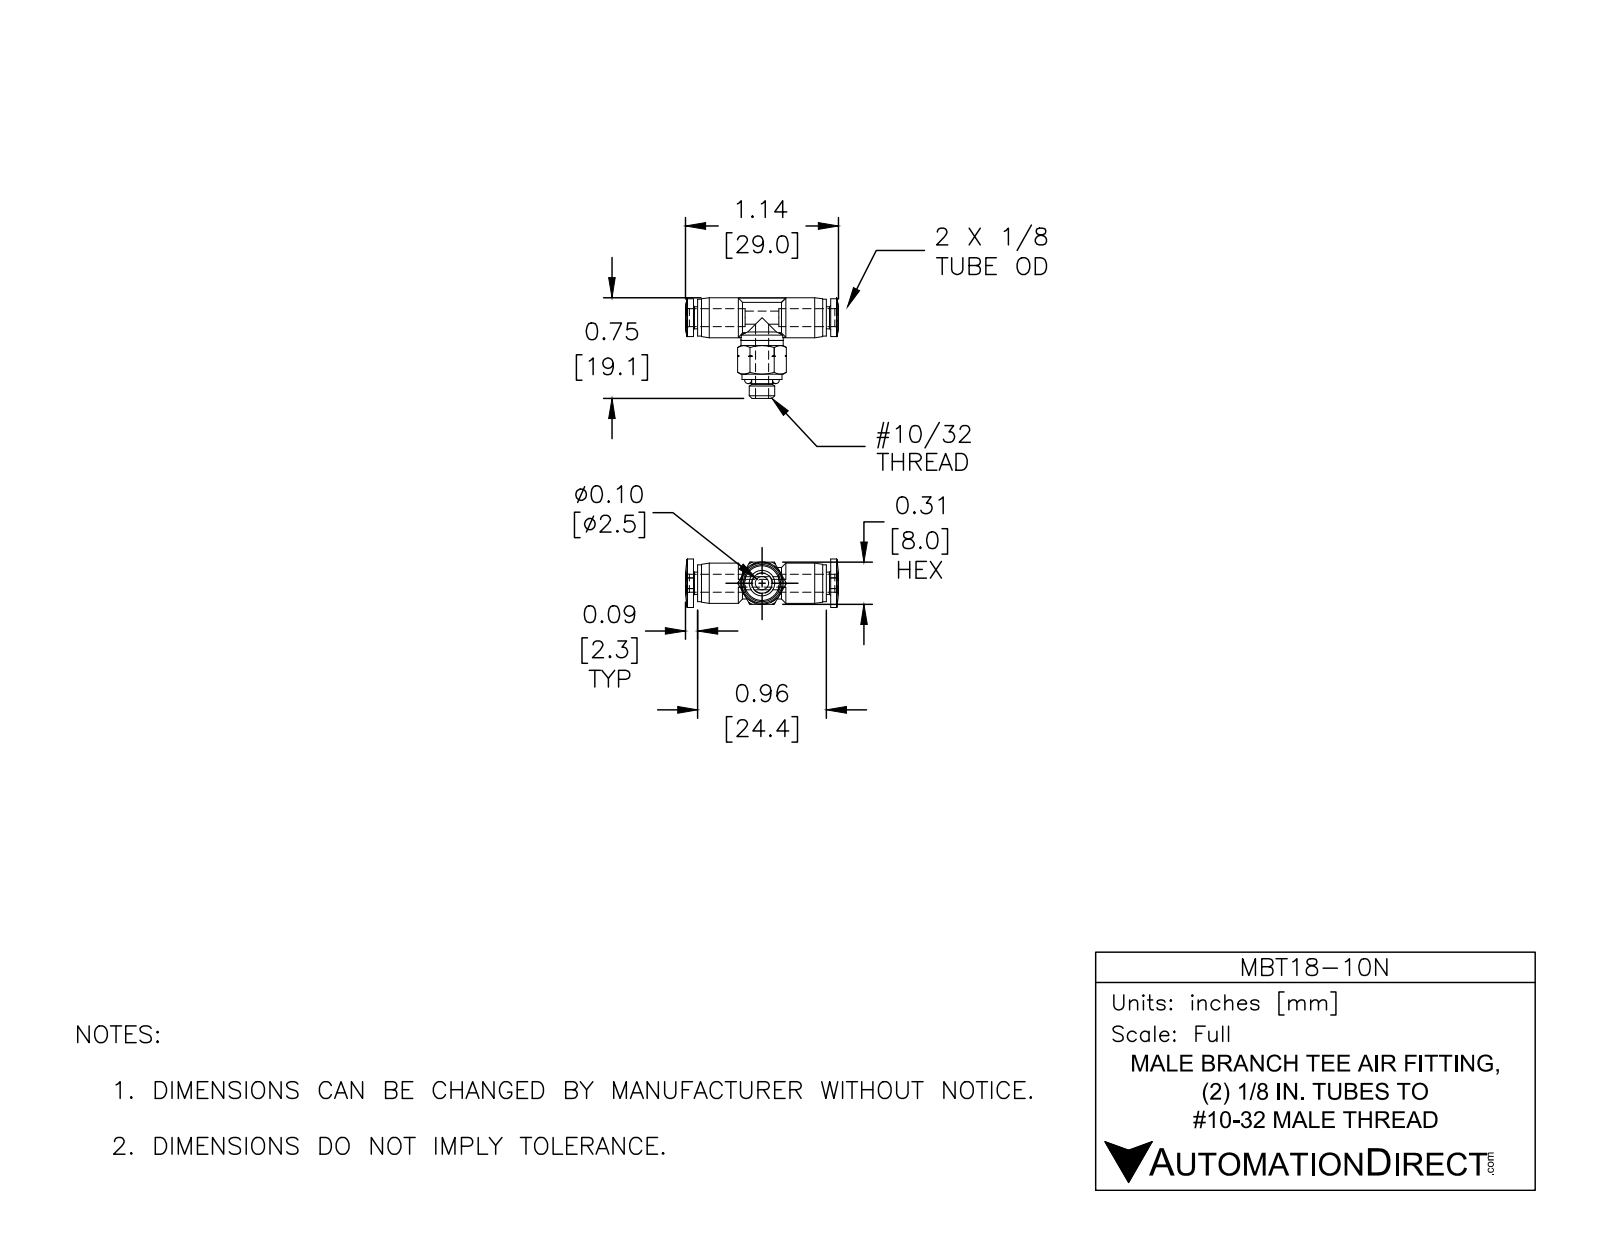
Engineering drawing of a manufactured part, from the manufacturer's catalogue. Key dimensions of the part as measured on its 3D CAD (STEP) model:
Part name (STEP PRODUCT): MBT18-10N
STEP written by: SolidWorks 2015 (CONFIG_CONTROL_DESIGN)
Units: inches
Bodies: 2 solids, 161 faces (32 planar, 46 cylindrical, 83 other)
Overall size (bounding box): 1.142 × 0.752 × 0.362
Volume: 0.083 in³ · Surface area: 2.615 in²
Round holes (diameter × count): ⌀0.098 ×2, ⌀0.134 ×1
Round bosses / shafts (diameter × count): ⌀0.299 ×2, ⌀0.315 ×1, ⌀0.315 ×1, ⌀0.276 ×1, ⌀0.236 ×1, ⌀0.19 ×1, ⌀0.165 ×1, ⌀0.156 ×1
Partial cylindrical surfaces — rounded edges, fillets, slot ends (radius × count): R0.142 ×2, R0.118 ×1
Main face-to-face distances: 0.315, 0.031, 0.992, 1.024, 0.961, 0.128, 0.187, 0.059, 0.02, 0.386
